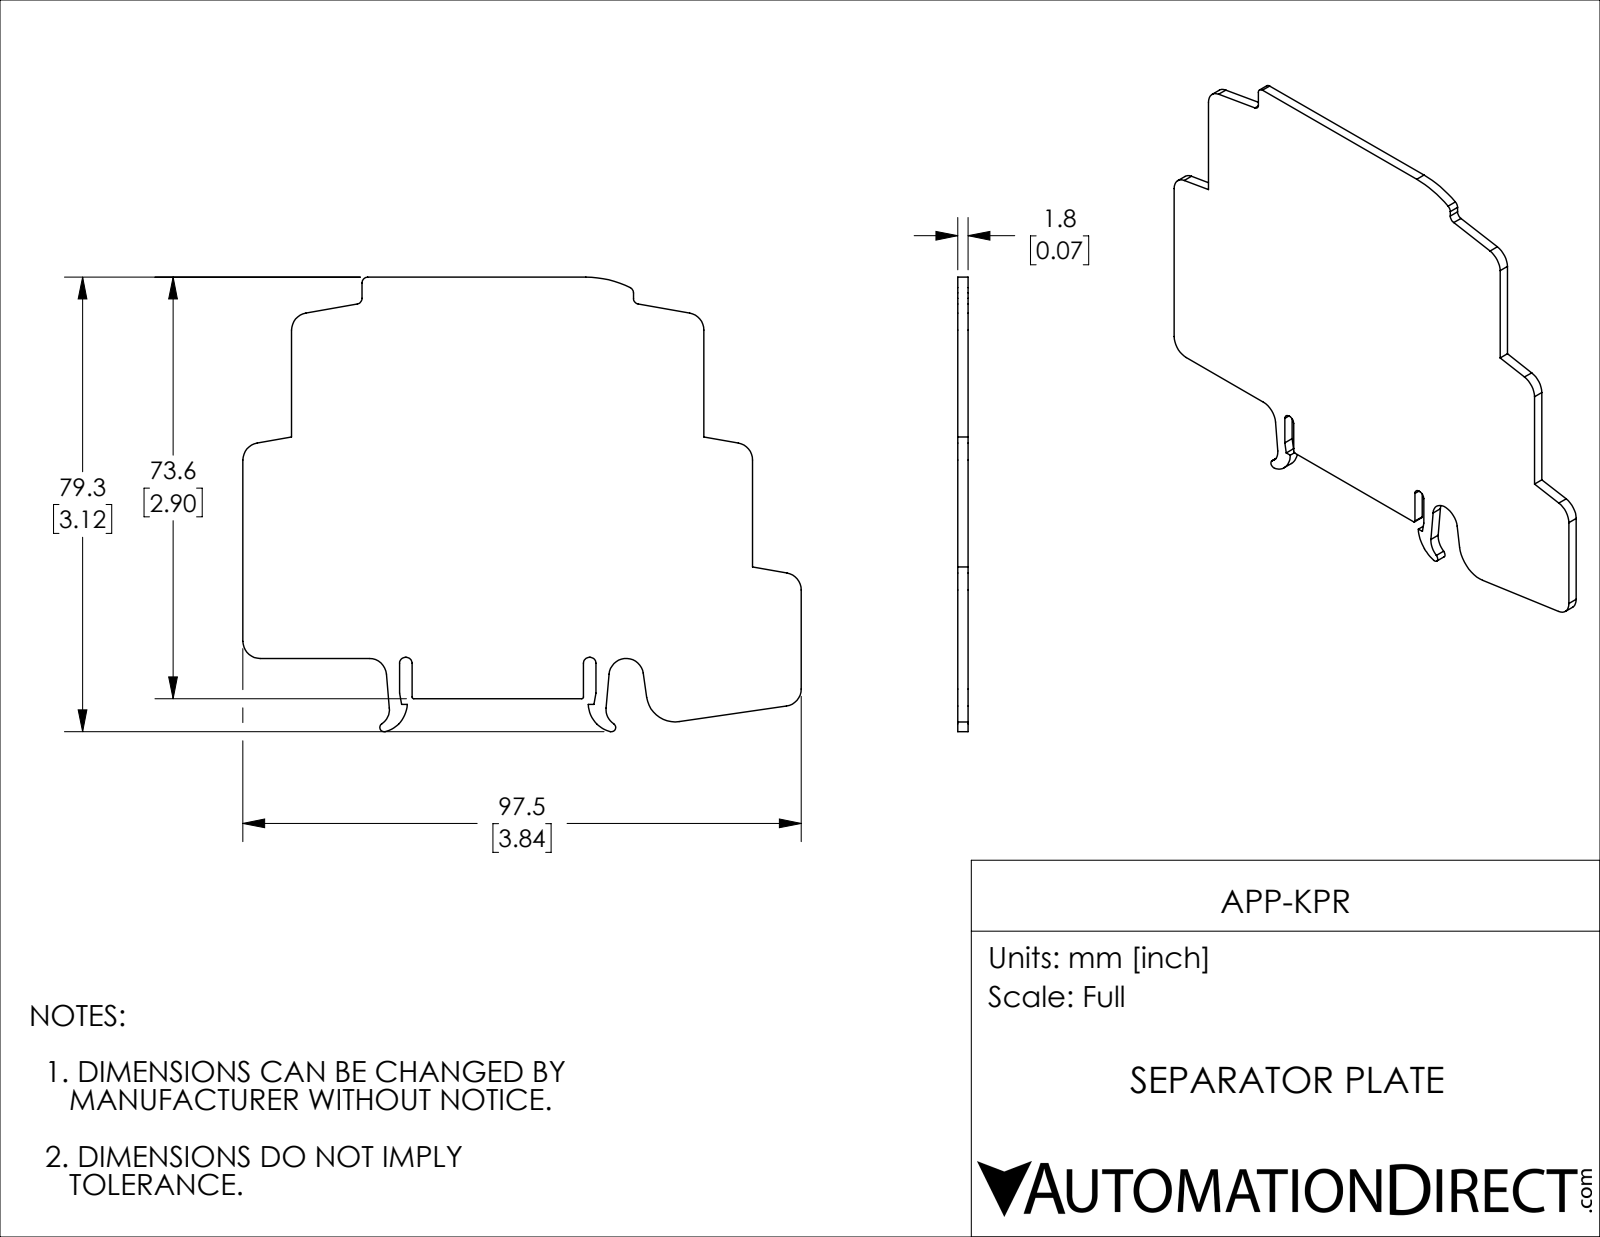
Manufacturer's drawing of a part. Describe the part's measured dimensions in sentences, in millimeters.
The part is named "APP-KPR". Its 3-D file was written by "SolidWorks 2021 (CONFIG_CONTROL_DESIGN)". It is 1 solid with 62 faces: 31 planar, 31 cylindrical and 0 other. Overall it measures 97.5 by 79.3 by 1.8 millimeters. Its volume is 10 700 cubic millimeters and its surface area 12 610 square millimeters. Partial cylindrical surfaces (rounded edges, fillets, slot ends): 11 of radius 3, 8 of radius 1, 3 of radius 5, 2 of radius 0.3, 2 of radius 0.8, 2 of radius 5.2, 1 of radius 17.2. The main face-to-face distances are 1.8, 8.5, 80.5, 73.6, 7, 66.5, 89, 72, 97.5, 89.
